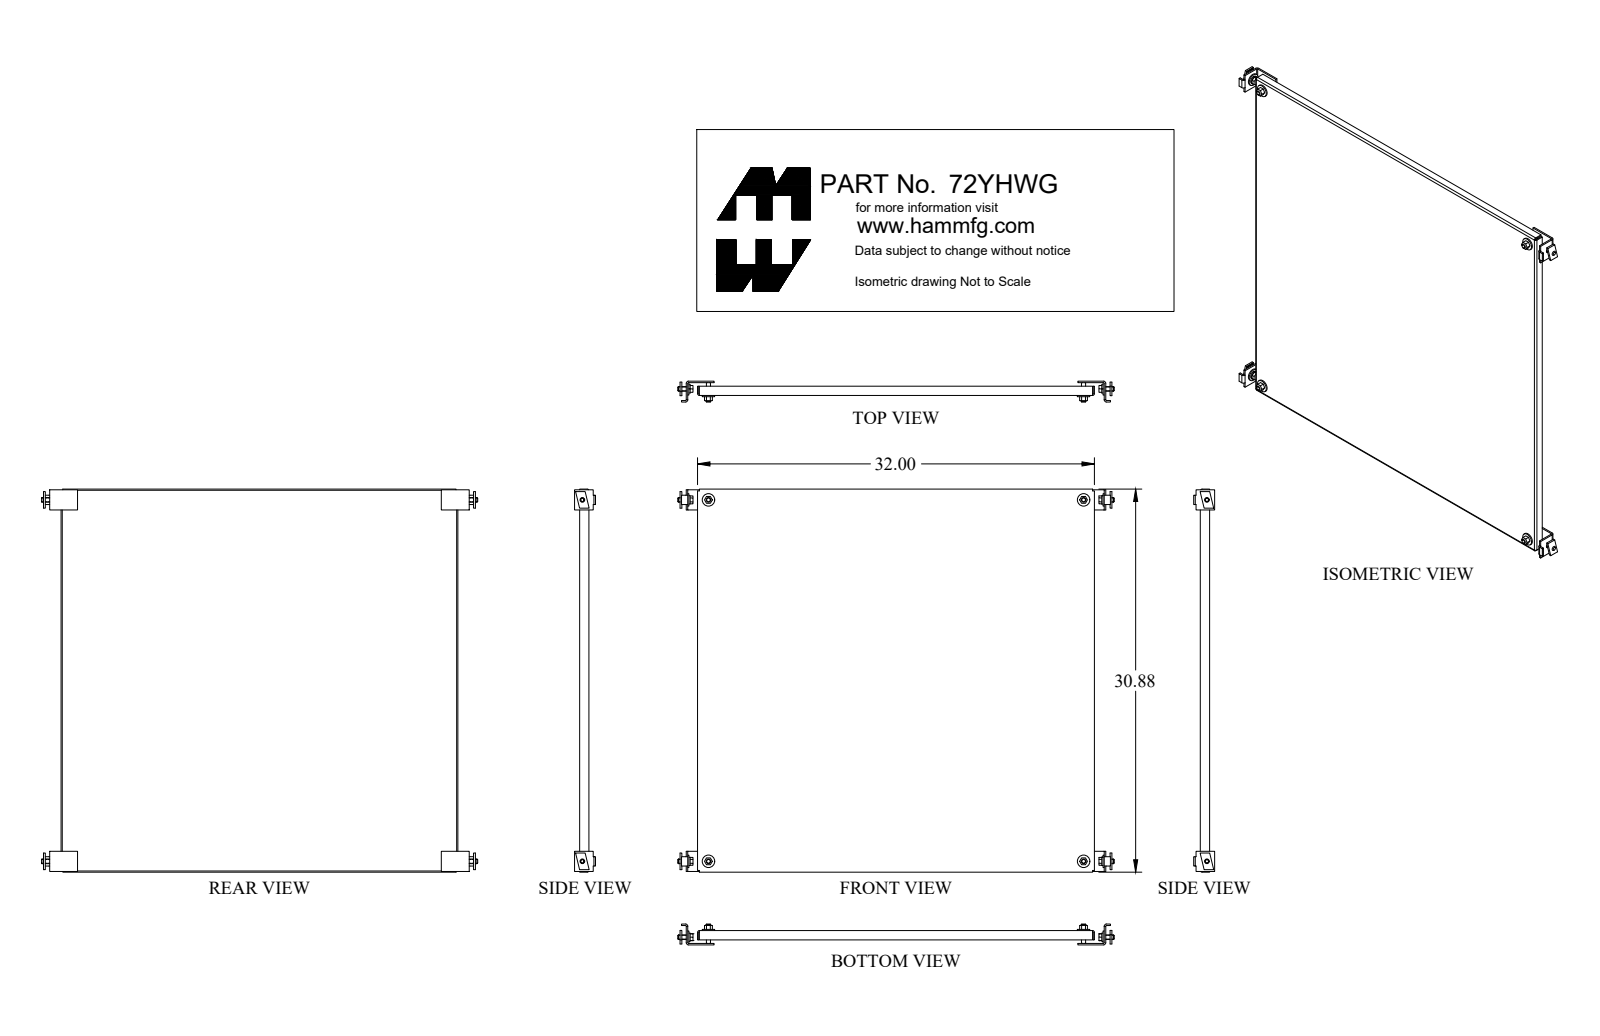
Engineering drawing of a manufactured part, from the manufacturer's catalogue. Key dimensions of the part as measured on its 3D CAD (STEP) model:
Part name (STEP PRODUCT): 72YHWG_Default
STEP written by: SolidWorks 2018 (CONFIG_CONTROL_DESIGN)
Units: inches
Bodies: 9 solids, 190 faces (94 planar, 64 cylindrical, 32 other)
Overall size (bounding box): 34.582 × 30.875 × 1.687
Volume: 104.7 in³ · Surface area: 2 204 in²
Round holes (diameter × count): ⌀0.563 ×4, ⌀0.437 ×2
Round bosses / shafts (diameter × count): ⌀0.65 ×4, ⌀0.375 ×4, ⌀0.33 ×4
Partial cylindrical surfaces — rounded edges, fillets, slot ends (radius × count): R0.048 ×4, R0.06 ×4, R0.143 ×4, R0.185 ×4
Main face-to-face distances: 0.095, 30.78, 31.905, 0.125, 30.875, 30.685, 32, 31.81, 1.032, 0.937
Hole centre spacings: 29.125, 30.25, 41.992, 29.13
